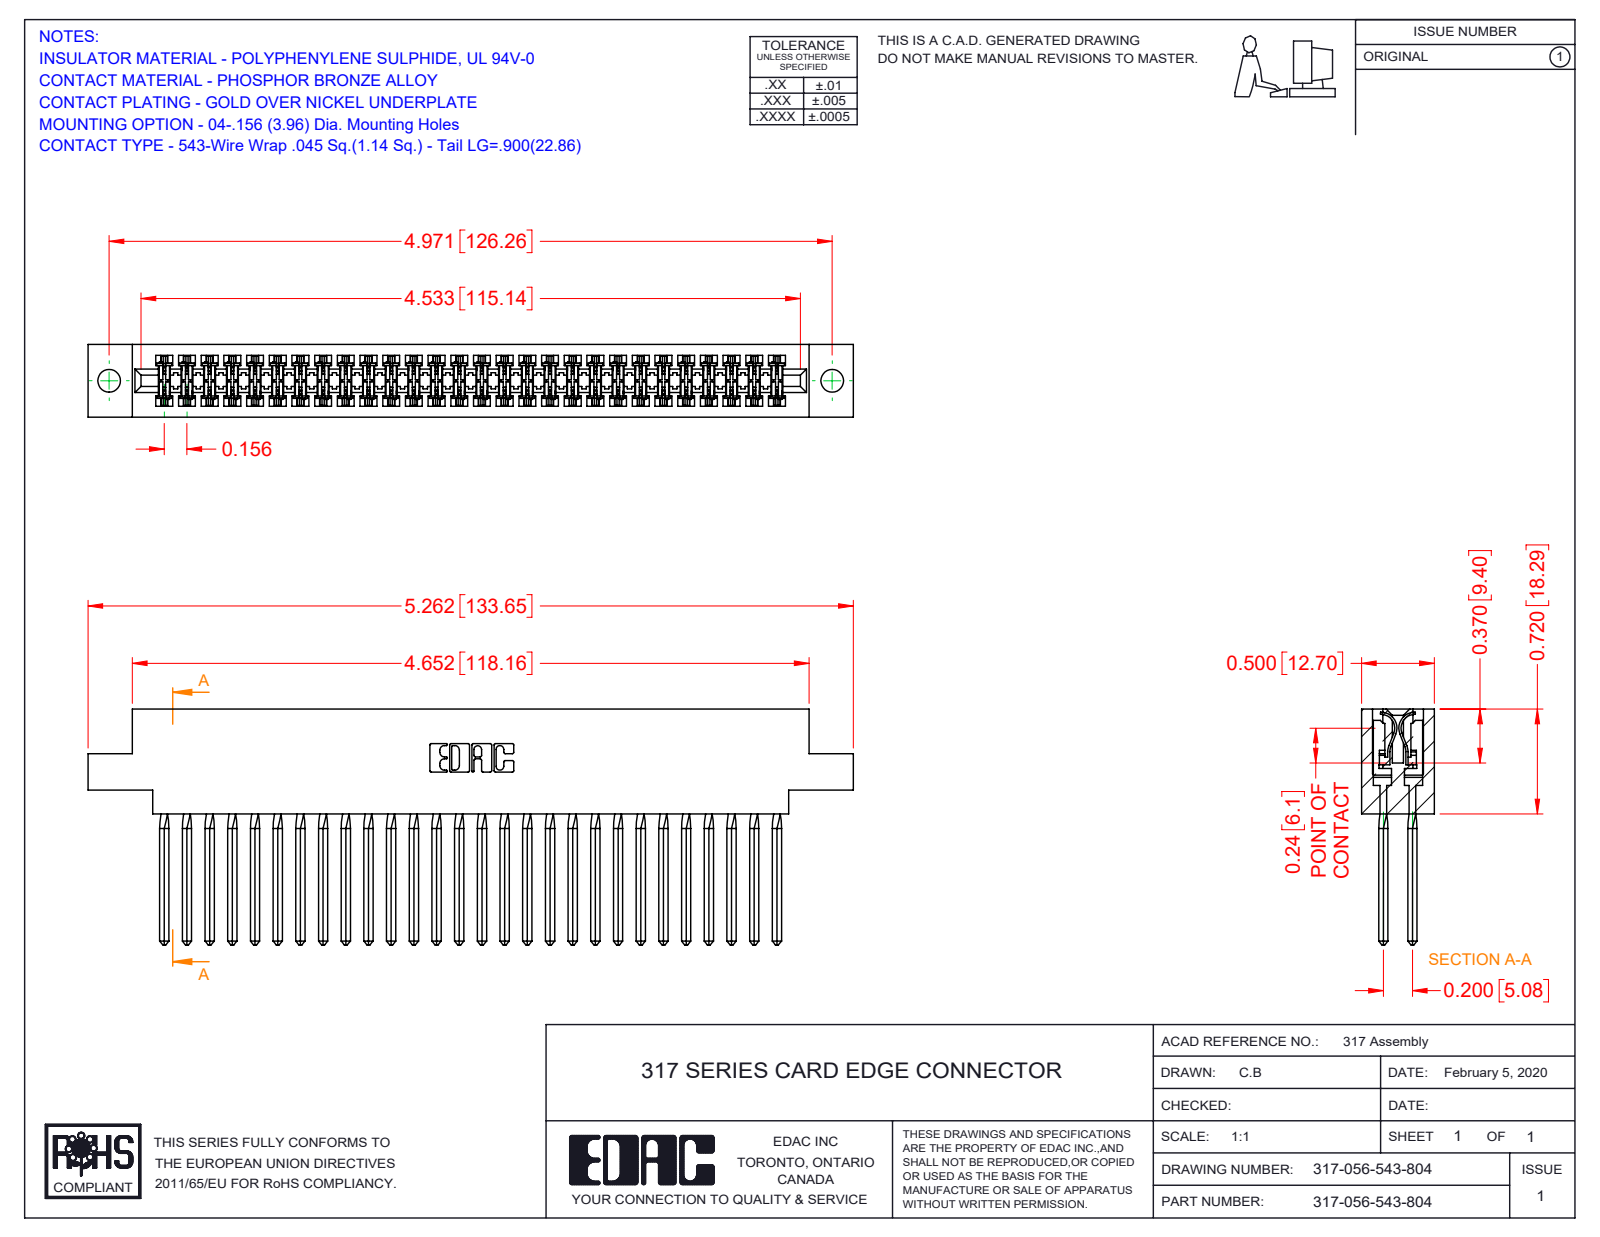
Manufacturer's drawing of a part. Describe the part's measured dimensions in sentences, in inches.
The part is named "317-056-543-804; 317 Part_.156 Dia - TH; 317-290-001_543". Its 3-D file was written by "SolidWorks 2016 (CONFIG_CONTROL_DESIGN)". It is 57 solids with 5086 faces: 4146 planar, 716 cylindrical and 224 other. Overall it measures 5.262 by 1.62 by 0.5 inches. Its volume is 1.352 cubic inches and its surface area 50.96 square inches. Round holes: 2 of diameter 0.156. Partial cylindrical surfaces (rounded edges, fillets, slot ends): 112 of radius 0.015, 22 of radius 0.01, 6 of radius 0.007, 6 of radius 0.031, 3 of radius 0.026, 2 of radius 0.095, 2 of radius 0.1, 2 of radius 0.11. The main face-to-face distances are 0.5, 0.075, 0.425, 0.35, 0.11, 0.195, 0.094, 0.2, 0.72, 0.115. The hole center spacings are 4.971.
